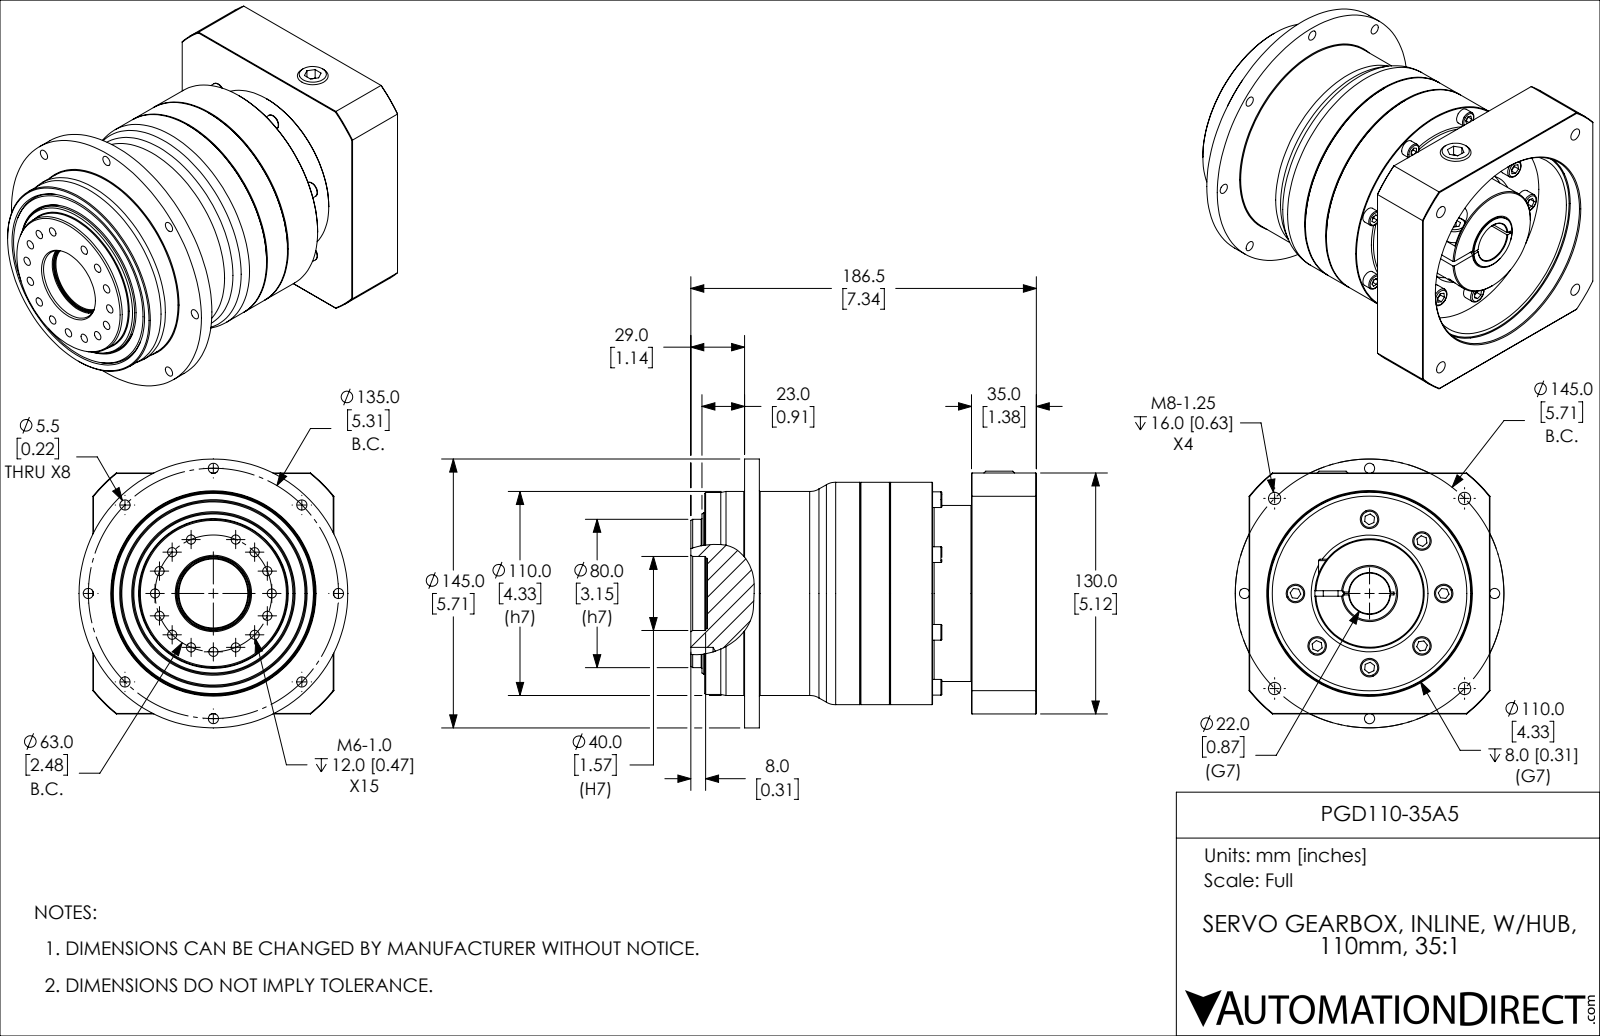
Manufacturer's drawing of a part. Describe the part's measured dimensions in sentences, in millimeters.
The part is named "PGD110-35A5". Its 3-D file was written by "SolidWorks 2015 (AUTOMOTIVE_DESIGN)". It is 11 solids with 578 faces: 302 planar, 193 cylindrical and 83 other. Overall it measures 186.5 by 145 by 145 millimeters. Its volume is 1 810 000 cubic millimeters and its surface area 169 611 square millimeters. Round holes: 11 of diameter 4.92, 8 of diameter 5.5, 4 of diameter 4.92, 3 of diameter 6.65, 2 of diameter 8, 1 of diameter 6.65, 1 of diameter 8.8, 1 of diameter 13, 1 of diameter 15, 1 of diameter 28, 1 of diameter 37.2, 1 of diameter 39.2. Round bosses or shafts: 7 of diameter 10, 1 of diameter 145, 1 of diameter 120, 1 of diameter 111, 1 of diameter 110, 1 of diameter 95, 1 of diameter 80, 1 of diameter 54.5. Partial cylindrical surfaces (rounded edges, fillets, slot ends): 7 of radius 4.25, 1 of radius 7, 1 of radius 83.2. The main face-to-face distances are 157.5, 4, 144.5, 29, 22, 129.4, 6, 122.5, 118.5, 26. The hole center spacings are 40.25, 62.62, 84.71, 97.35, 12.29, 52.38, 74.49, 44.54.
